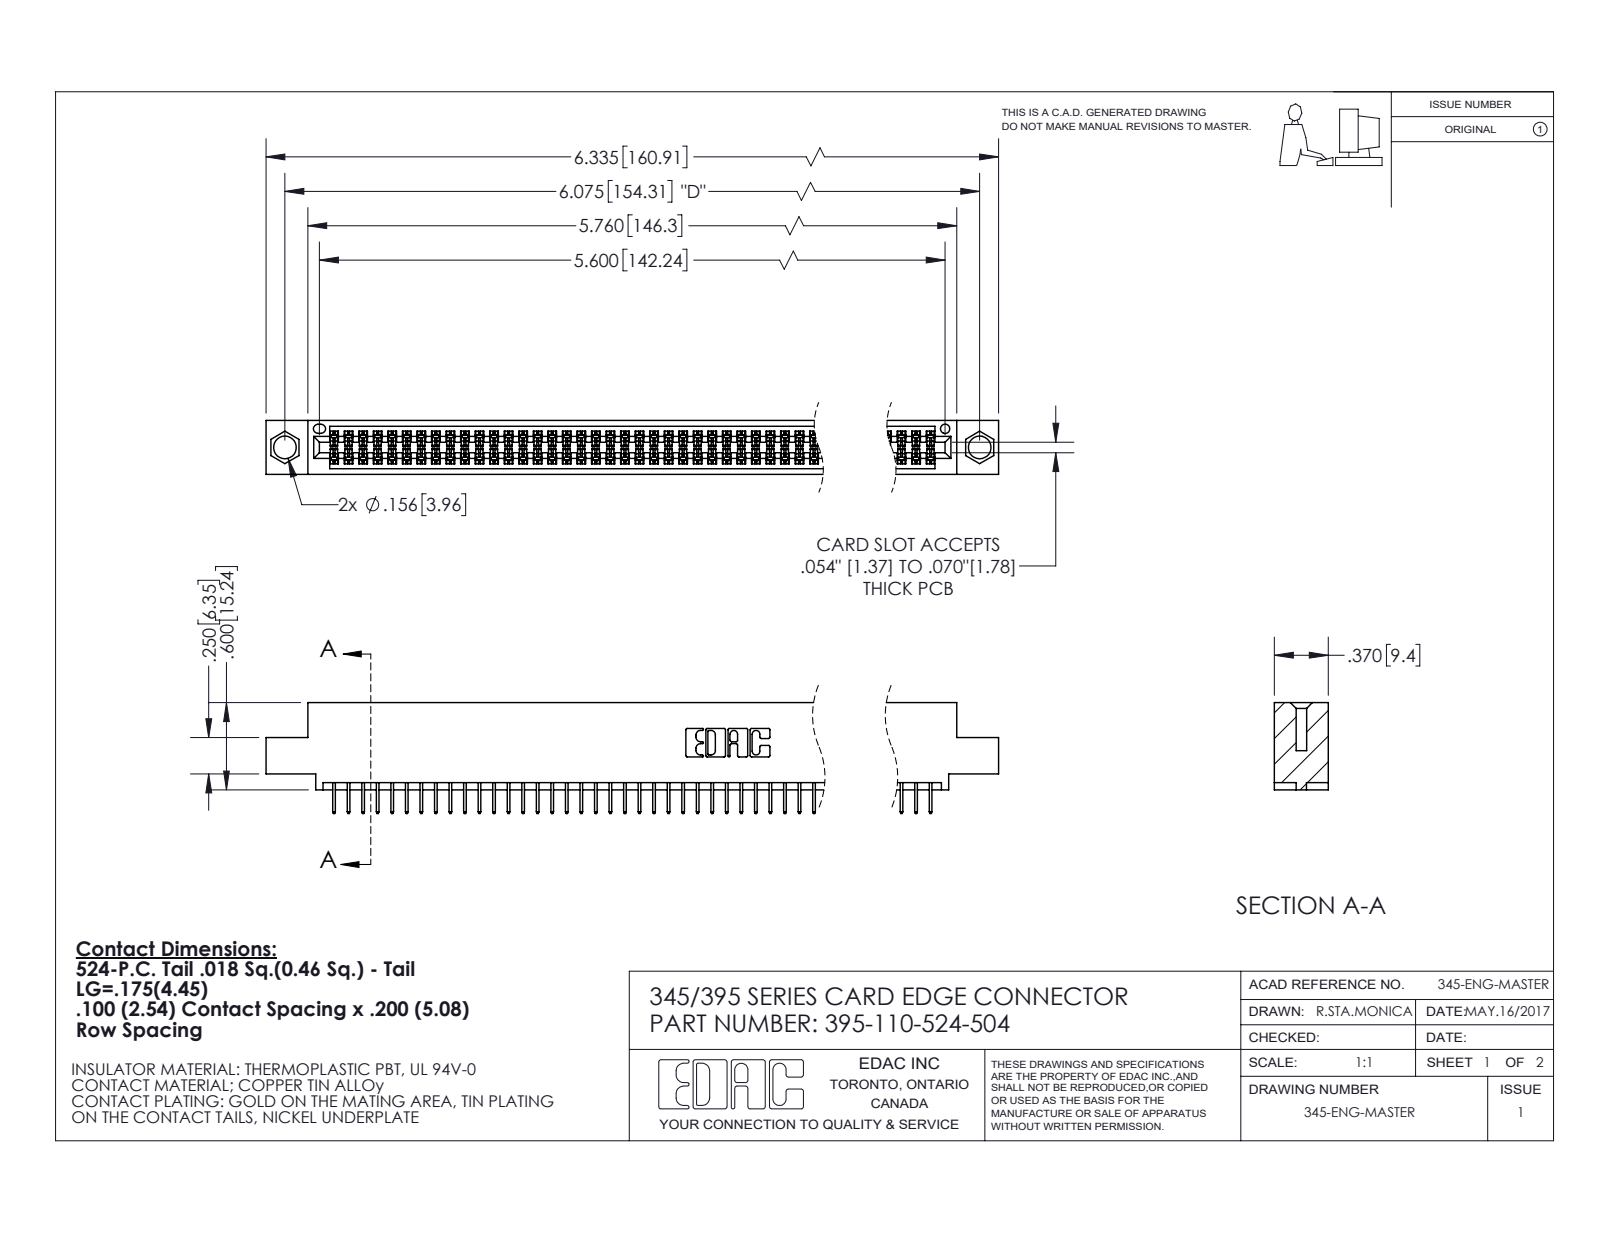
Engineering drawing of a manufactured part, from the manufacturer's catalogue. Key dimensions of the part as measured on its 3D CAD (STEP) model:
Part name (STEP PRODUCT): 395-110-524-504; 345-292-001_345-293-124; 345 Part_0.110 Offset - 0.156 Dia-TI
STEP written by: SolidWorks 2020 (CONFIG_CONTROL_DESIGN)
Units: inches
Bodies: 111 solids, 6084 faces (4388 planar, 1696 cylindrical, 0 other)
Overall size (bounding box): 6.335 × 0.762 × 0.37
Volume: 0.94 in³ · Surface area: 34.92 in²
Round holes (diameter × count): ⌀0.156 ×2, ⌀0.064 ×1
Partial cylindrical surfaces — rounded edges, fillets, slot ends (radius × count): R0.006 ×165, R0.01 ×22, R0.007 ×6, R0.031 ×6, R0.026 ×3, R0.014 ×2, R0.019 ×2, R0.022 ×2
Main face-to-face distances: 0.072, 0.298, 0.2, 0.37, 0.098, 0.272, 0.025, 0.225, 0.072, 0.175
Hole centre spacings: 0.27, 5.839, 6.075
